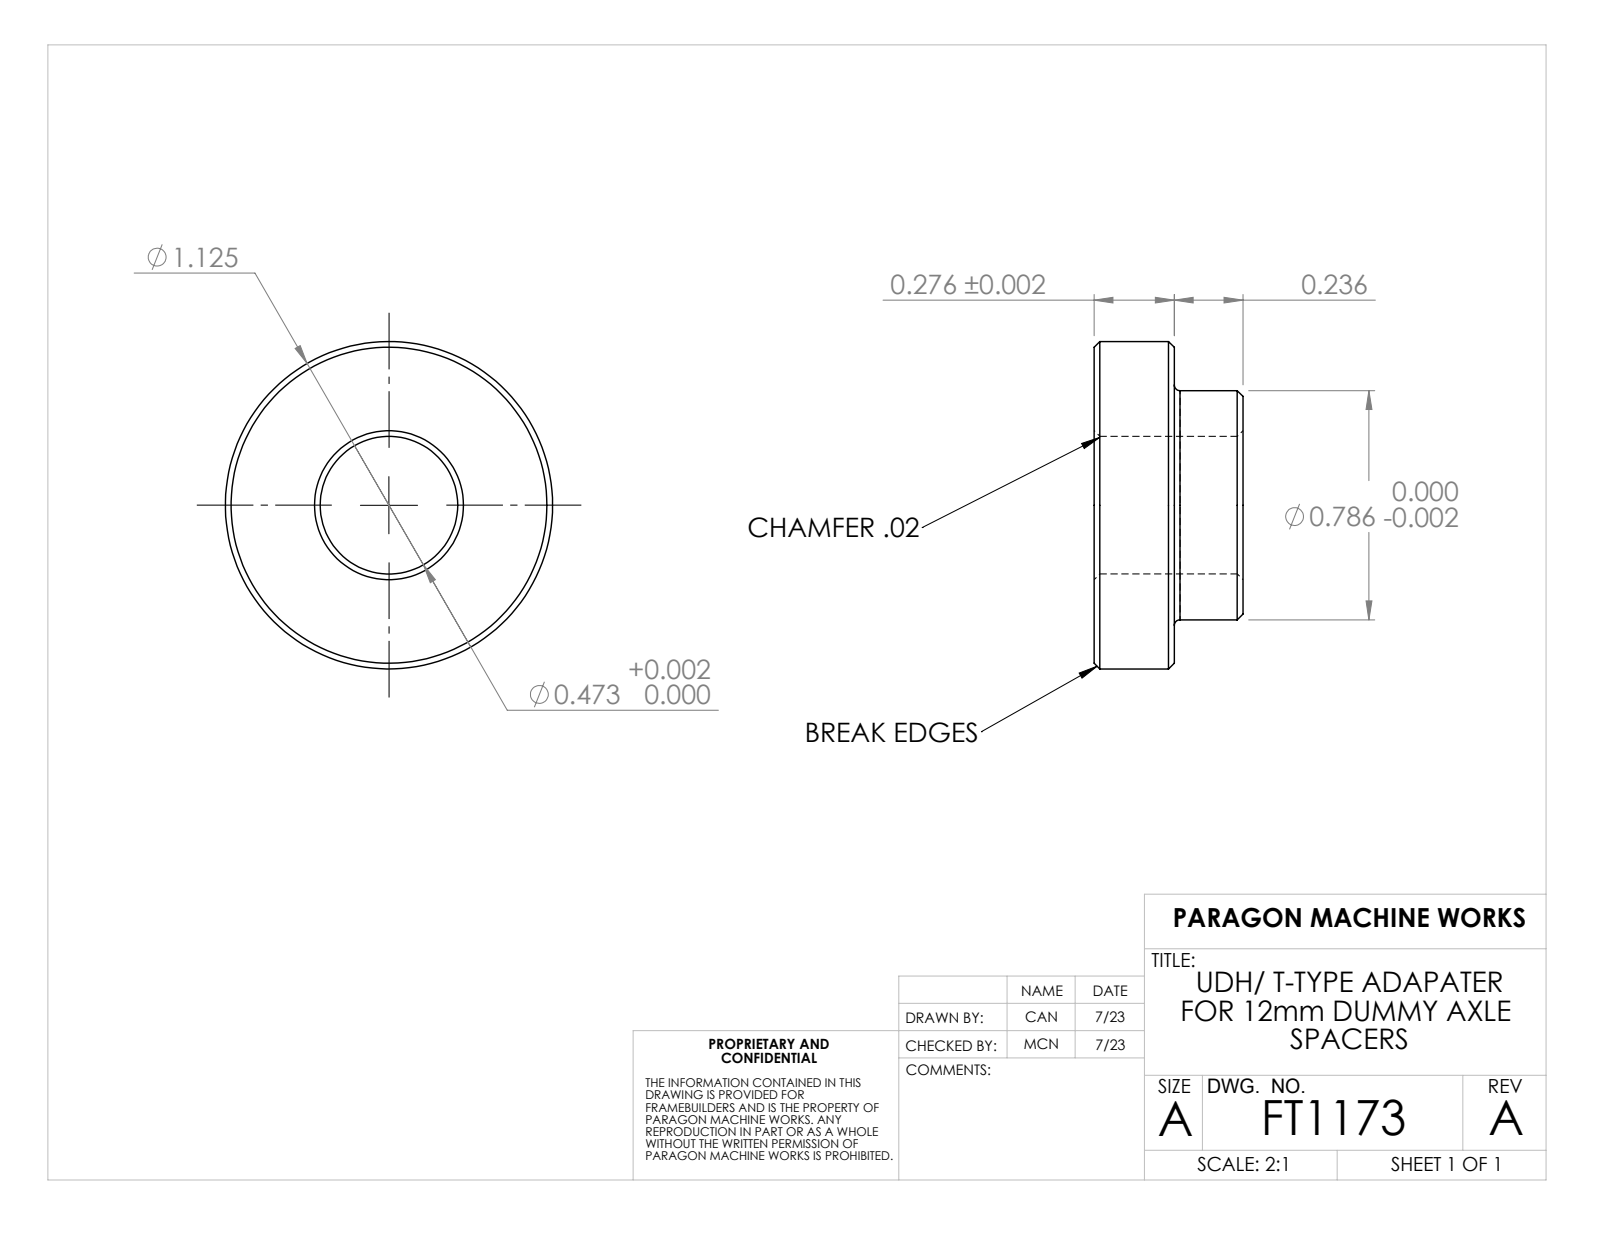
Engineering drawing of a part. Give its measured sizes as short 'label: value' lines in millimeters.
name: FT1173
written by: SolidWorks 2023 (AUTOMOTIVE_DESIGN)
unit: mm
bodies: 1 solid, 21 faces (3 planar, 6 cylindrical, 12 other)
size: 28.57 × 28.57 × 13
volume: 4 866 mm³; area: 2 445 mm²
holes: 1× ⌀12.01
bosses: 1× ⌀28.58, 1× ⌀20
face distances: 7, 6, 13
